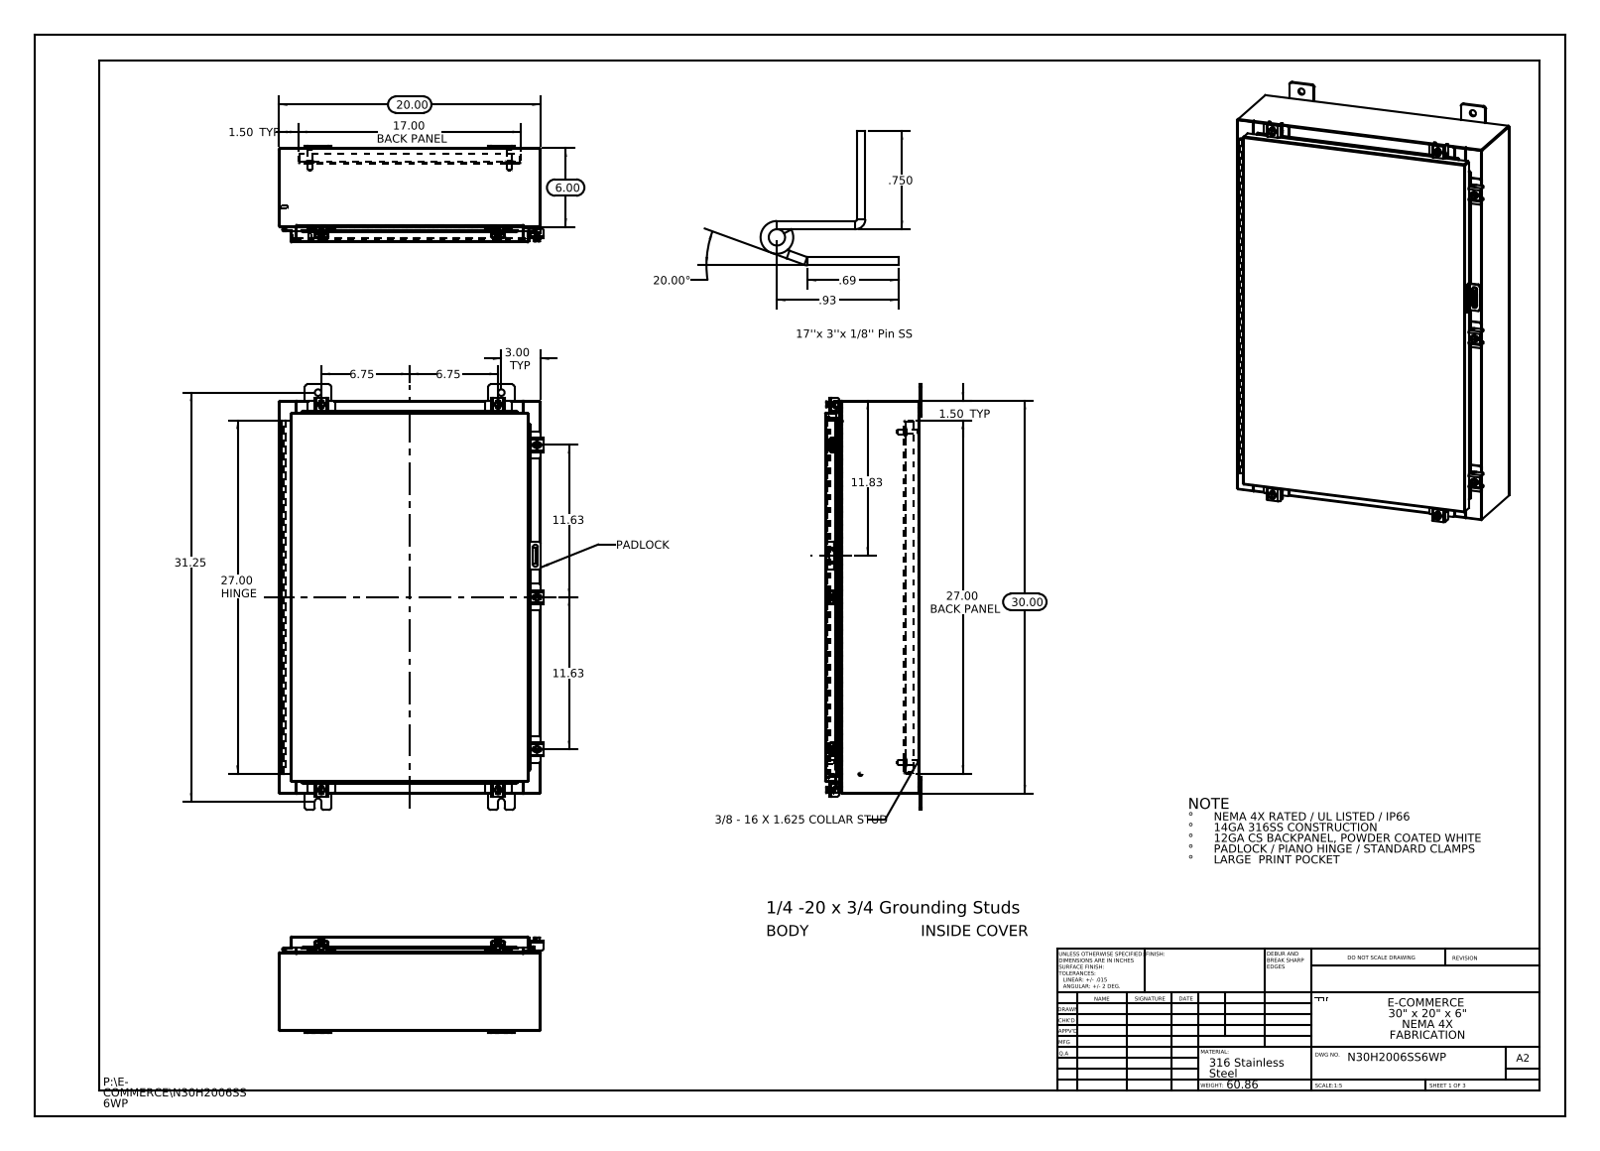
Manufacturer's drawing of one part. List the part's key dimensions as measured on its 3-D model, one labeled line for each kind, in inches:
Part name (STEP PRODUCT): N30H2006SS6WP Hinge Enclosure Side2; N30H2006SS6WP Body; Quarter-20 CD Stud; N30H2006SS6WP 22104005_DEFAULT (+8 more)
STEP written by: SolidWorks 2013 (CONFIG_CONTROL_DESIGN)
Units: inches
Bodies: 54 solids, 2016 faces (1062 planar, 838 cylindrical, 116 other)
Overall size (bounding box): 32.5 × 20.211 × 7.389
Volume: 214.2 in³ · Surface area: 5 348 in²
Round holes (diameter × count): ⌀0.5 ×8, ⌀0.213 ×7, ⌀0.26 ×7, ⌀0.125 ×2, ⌀0.125 ×1
Round bosses / shafts (diameter × count): ⌀0.25 ×8, ⌀0.5 ×7, ⌀0.399 ×7, ⌀0.625 ×4, ⌀0.375 ×4, ⌀0.33 ×4, ⌀0.315 ×2, ⌀0.236 ×2
Partial cylindrical surfaces — rounded edges, fillets, slot ends (radius × count): R0.06 ×34, R0.013 ×27, R0.19 ×24, R0.088 ×21, R0.12 ×14, R0.141 ×14, R0.05 ×11, R0.08 ×10
Main face-to-face distances: 0.075, 7.126, 7.051, 7.201, 0.104, 1, 1.075, 6.051, 6.126, 1.179
Hole centre spacings: 27.365, 30.898, 0.431, 0.934, 1.858, 2.275, 2.276, 2.327
